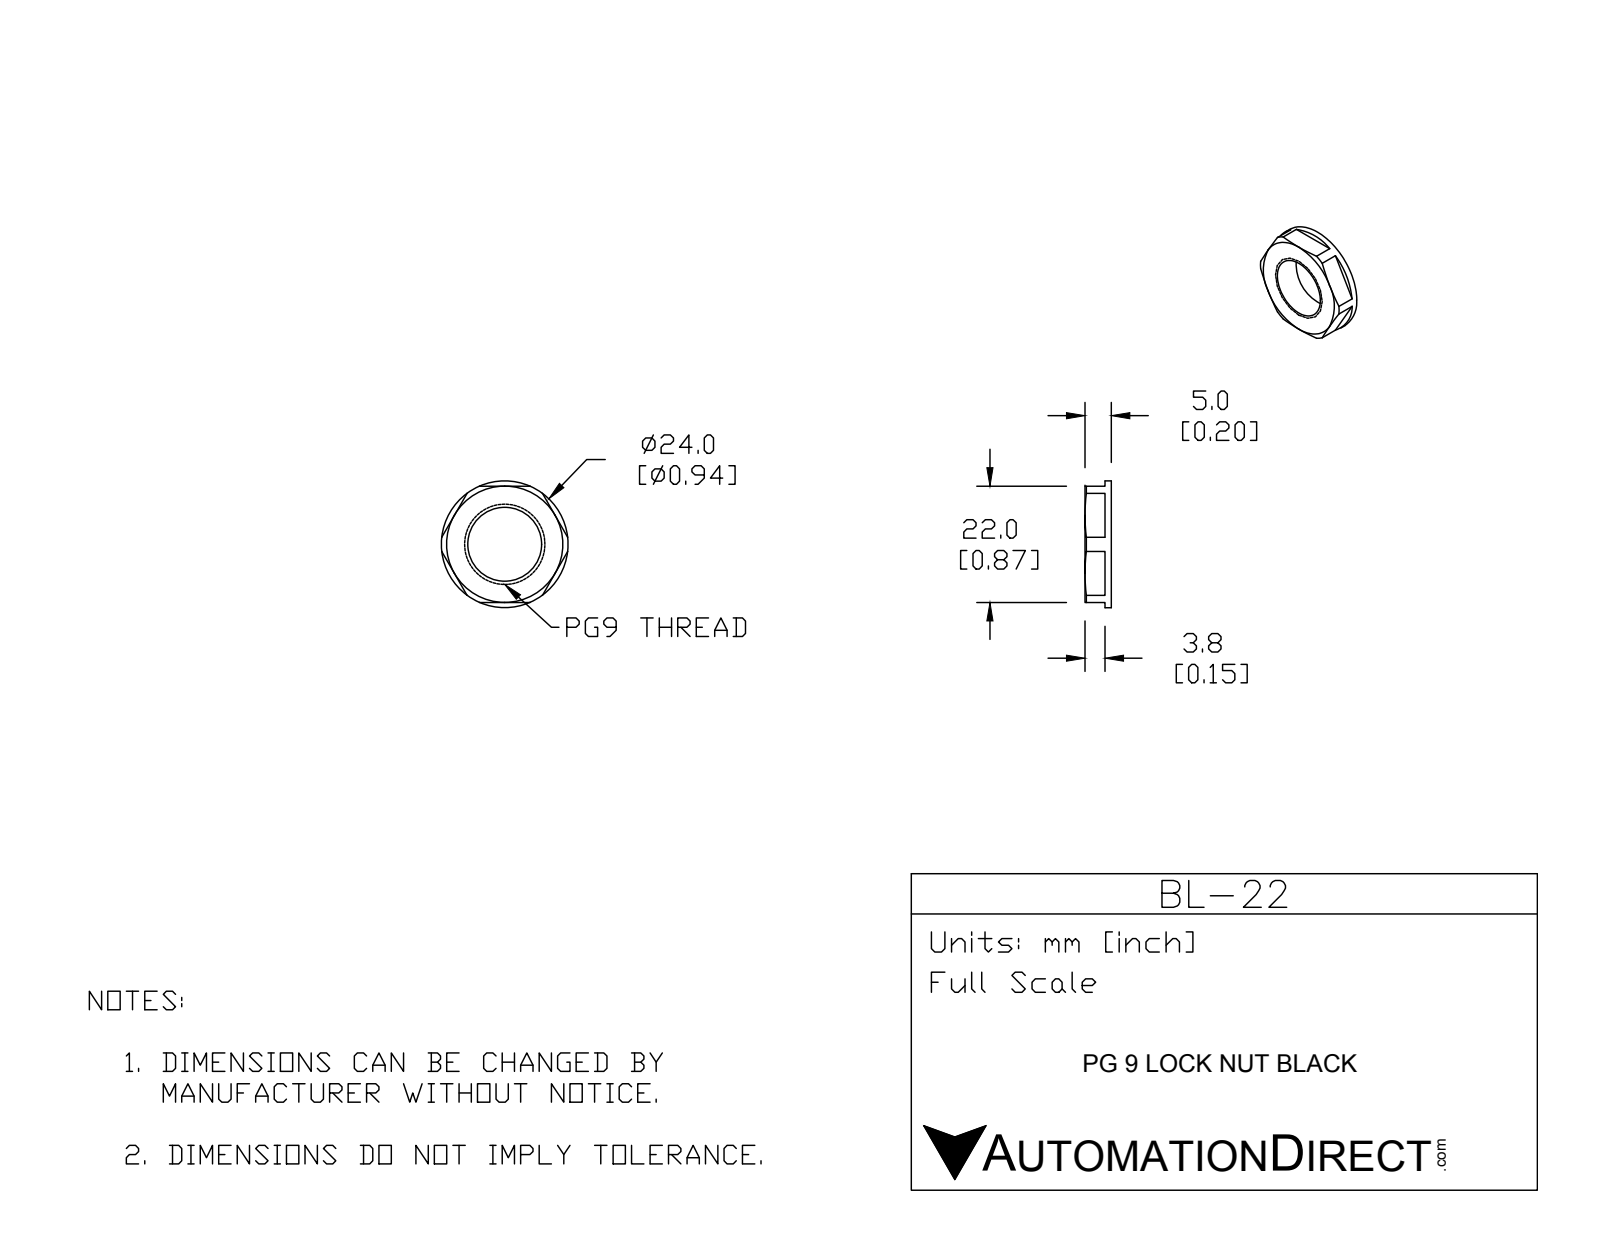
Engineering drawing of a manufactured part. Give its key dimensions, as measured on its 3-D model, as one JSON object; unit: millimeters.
{"part_name": "BL-22", "step_written_by": "SolidWorks 2015 (CONFIG_CONTROL_DESIGN)", "units": "millimeters", "bodies": {"solids": 1, "faces": 33, "planar": 17, "cylindrical": 10, "other": 6}, "overall_size": [24, 24, 5], "volume_mm3": 1340, "surface_area_mm2": 1183, "round_holes": [[1.5, 3], [14, 1]], "round_bosses_or_shafts": [[24, 1]], "face_to_face_distances": [5, 22, 1.2, 3.8, 0.9, 4.7], "hole_center_spacings": [10.55, 18.28, 10.56, 18.27]}
